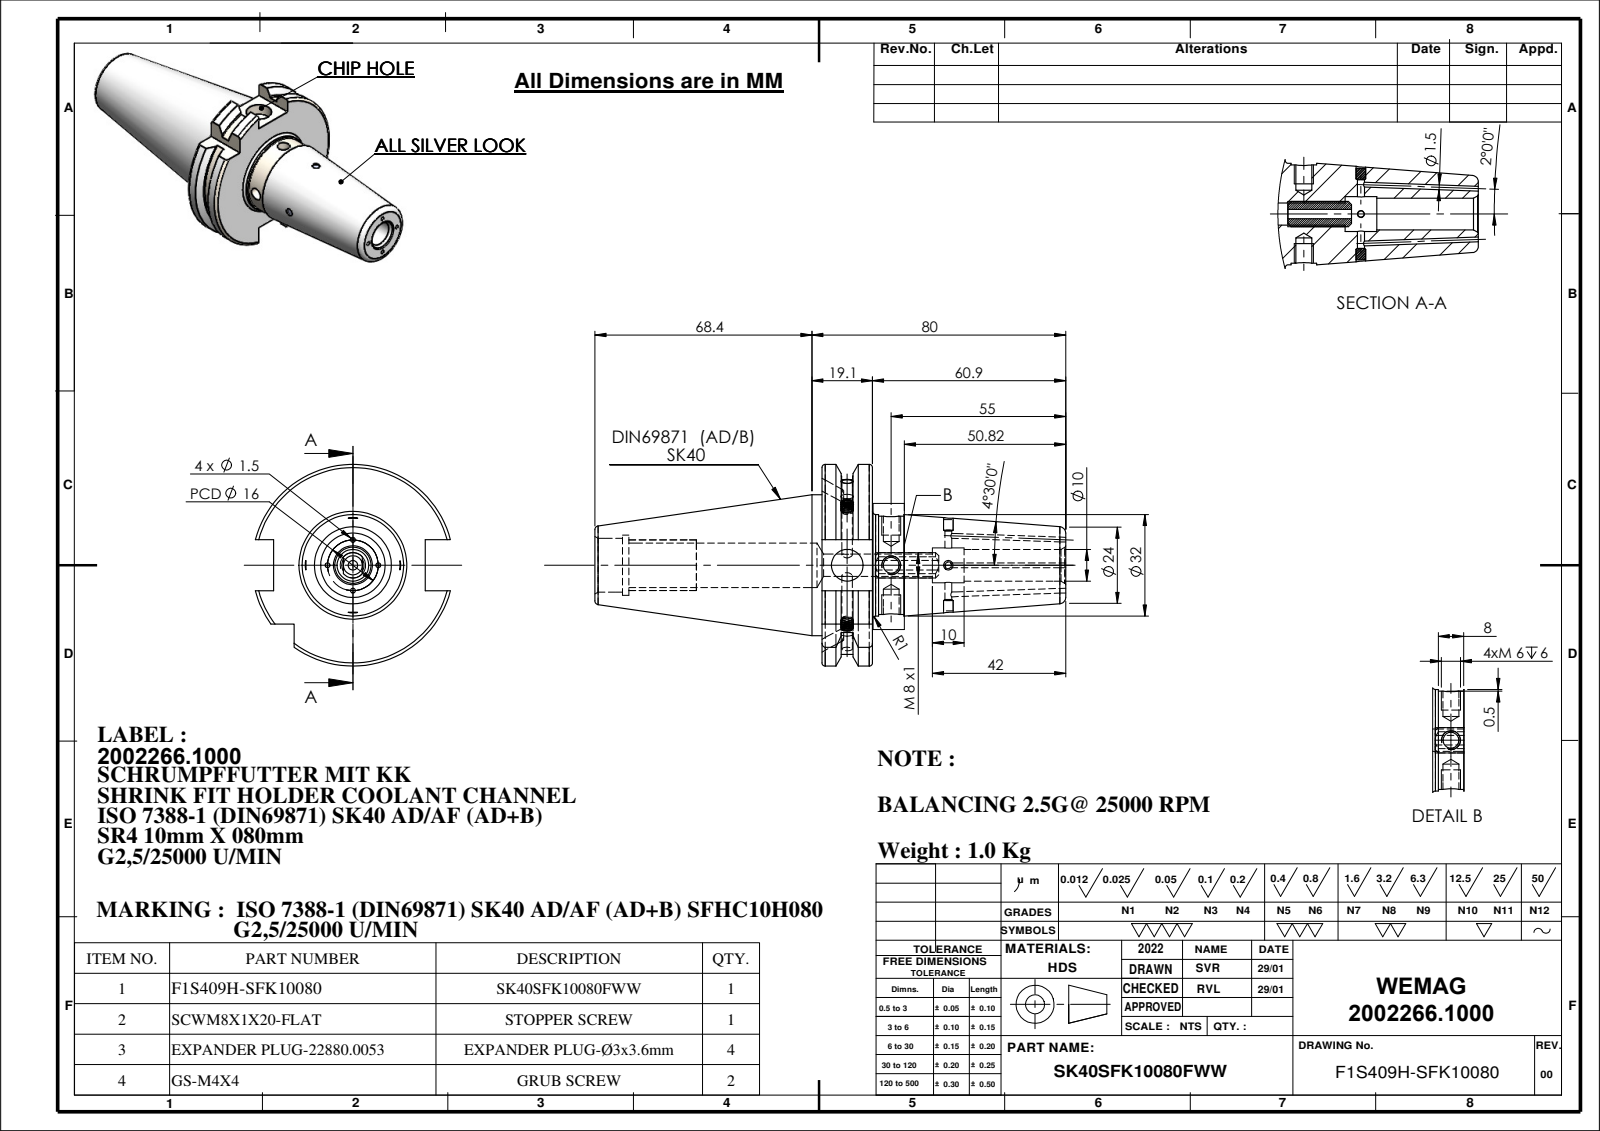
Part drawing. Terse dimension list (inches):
name: SK40SFK10080FWW; SCWM8X1X20-FLAT; 91406-SR410080; GS-M4X4_DIN 913 - M4 x 4-N (+1 more)
written by: SolidWorks 2018 (CONFIG_CONTROL_DESIGN)
unit: in
bodies: 8 solids, 289 faces (62 planar, 103 cylindrical, 124 other)
size: 5.843 × 2.502 × 2.42
volume: 8.232 in³; area: 47.42 in²
holes: 4× ⌀0.059, 3× ⌀0.118, 2× ⌀0.087, 2× ⌀0.197, 1× ⌀0.13, 1× ⌀0.276, 1× ⌀0.393, 1× ⌀0.394, 1× ⌀0.433, 1× ⌀0.551, 1× ⌀0.669, 1× ⌀0.748
bosses: 2× ⌀0.157, 1× ⌀1.75, 1× ⌀1.26, 1× ⌀1.22
rounds: 1× R0.157, 1× R1.107, 1× R1.251
face distances: 0.626, 2.398, 3.024, 0.634, 1.882, 1.016, 2.819, 3.445, 5.843, 0.421
hole spacings: 0.709, 0.545, 1.254
